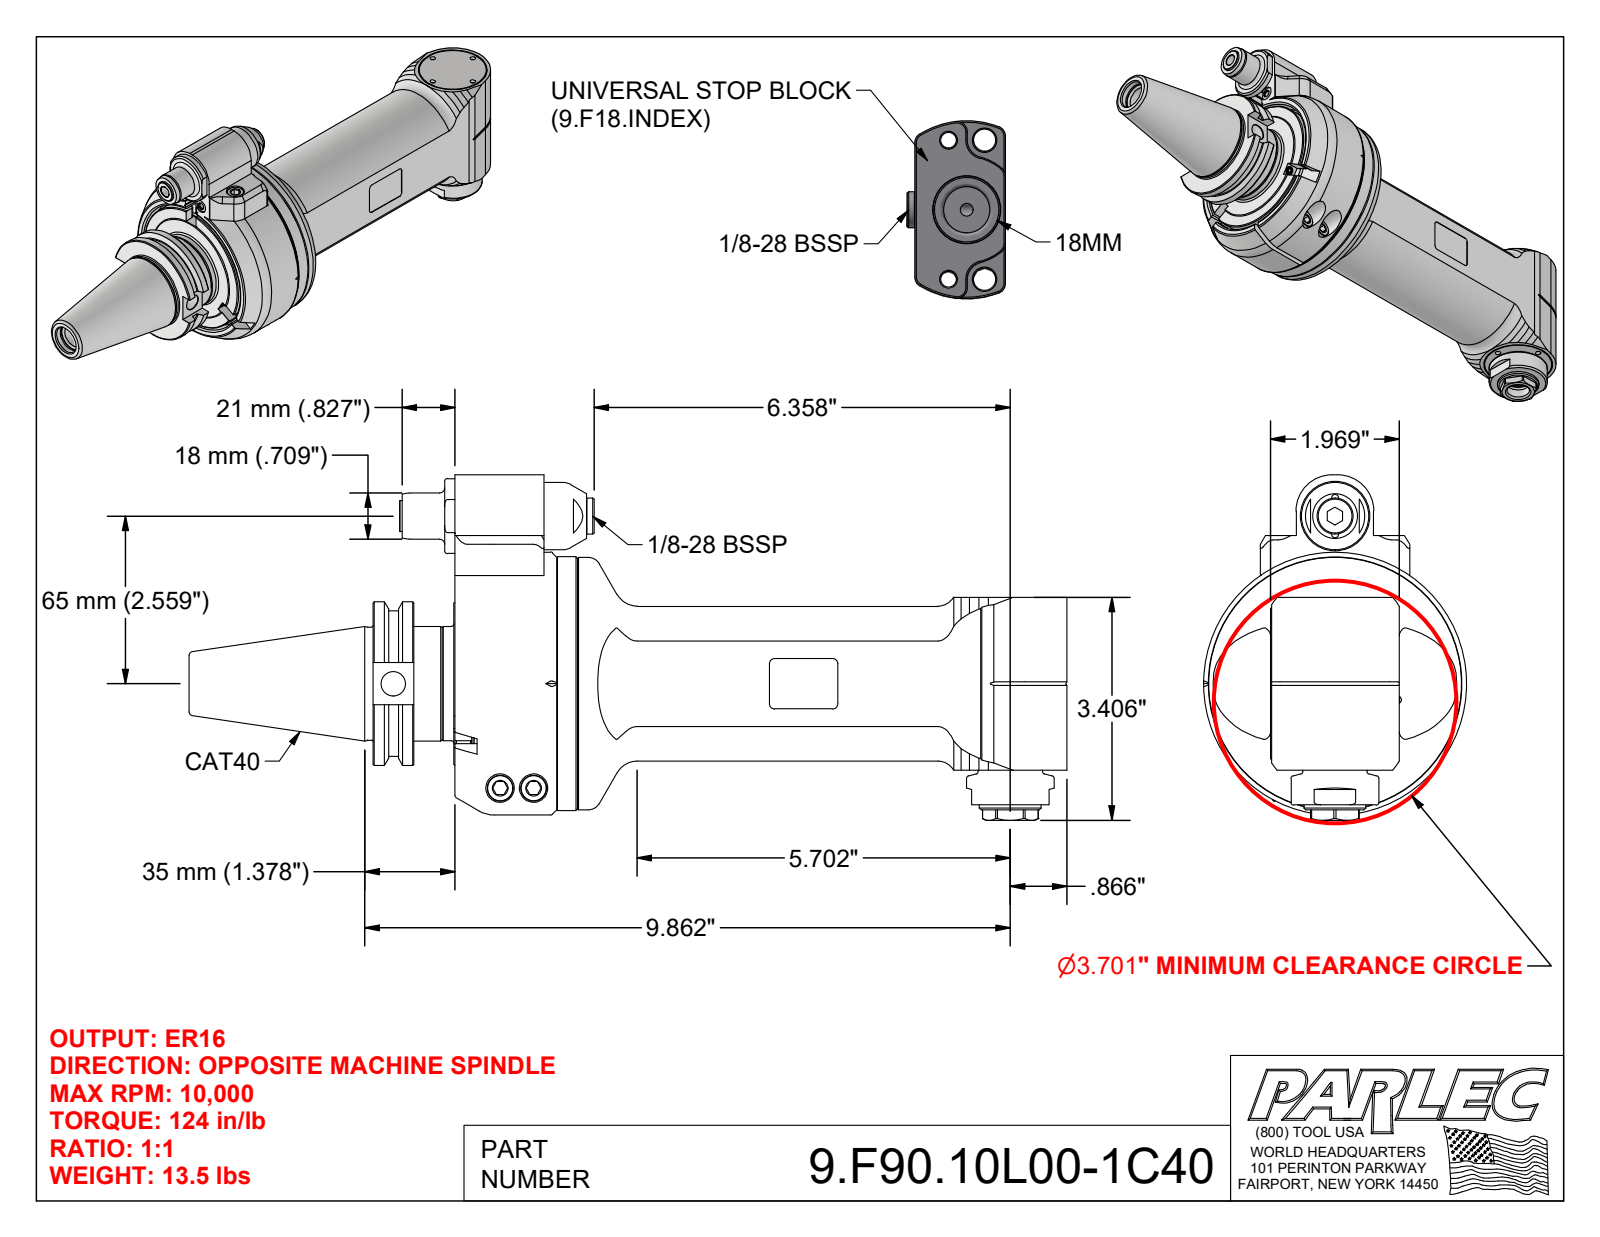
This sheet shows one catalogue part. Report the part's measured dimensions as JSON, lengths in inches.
{"part_name": "9.F90.10L00-1C40; 9_F90_10L00; 9_GA1_446_2 (EVO, Type 1, C40, 65mm, 35mm)", "step_written_by": "Autodesk Inventor 2022 (AUTOMOTIVE_DESIGN)", "units": "inches", "bodies": {"solids": 6, "faces": 698, "planar": 298, "cylindrical": 191, "other": 209}, "overall_size": [13.415, 5.276, 4.016], "volume_in3": 65.67, "surface_area_in2": 253.7, "round_holes": [[0.335, 20], [0.126, 8], [0.197, 3], [0.256, 3], [0.433, 3], [0.102, 2], [0.13, 2], [0.165, 2], [0.315, 2], [0.409, 2], [0.492, 2], [0.512, 2]], "round_bosses_or_shafts": [[0.394, 4], [0.709, 2], [0.472, 2], [0.315, 2], [0.236, 2], [0.098, 2], [4.016, 1], [3.874, 1]], "partial_cylinders_radius": [[0.039, 14], [0.079, 12], [0.118, 6], [0.157, 4], [0.016, 2], [0.02, 2], [0.315, 2], [0.551, 2]], "face_to_face_distances": [0.02, 1.969, 0.295, 0.039, 0.276, 1.555, 1.26, 0.335, 1.575, 0.315], "hole_center_spacings": [1.516, 2.144, 1.824, 3.002, 0.835, 2.651, 2.914, 3.031]}
